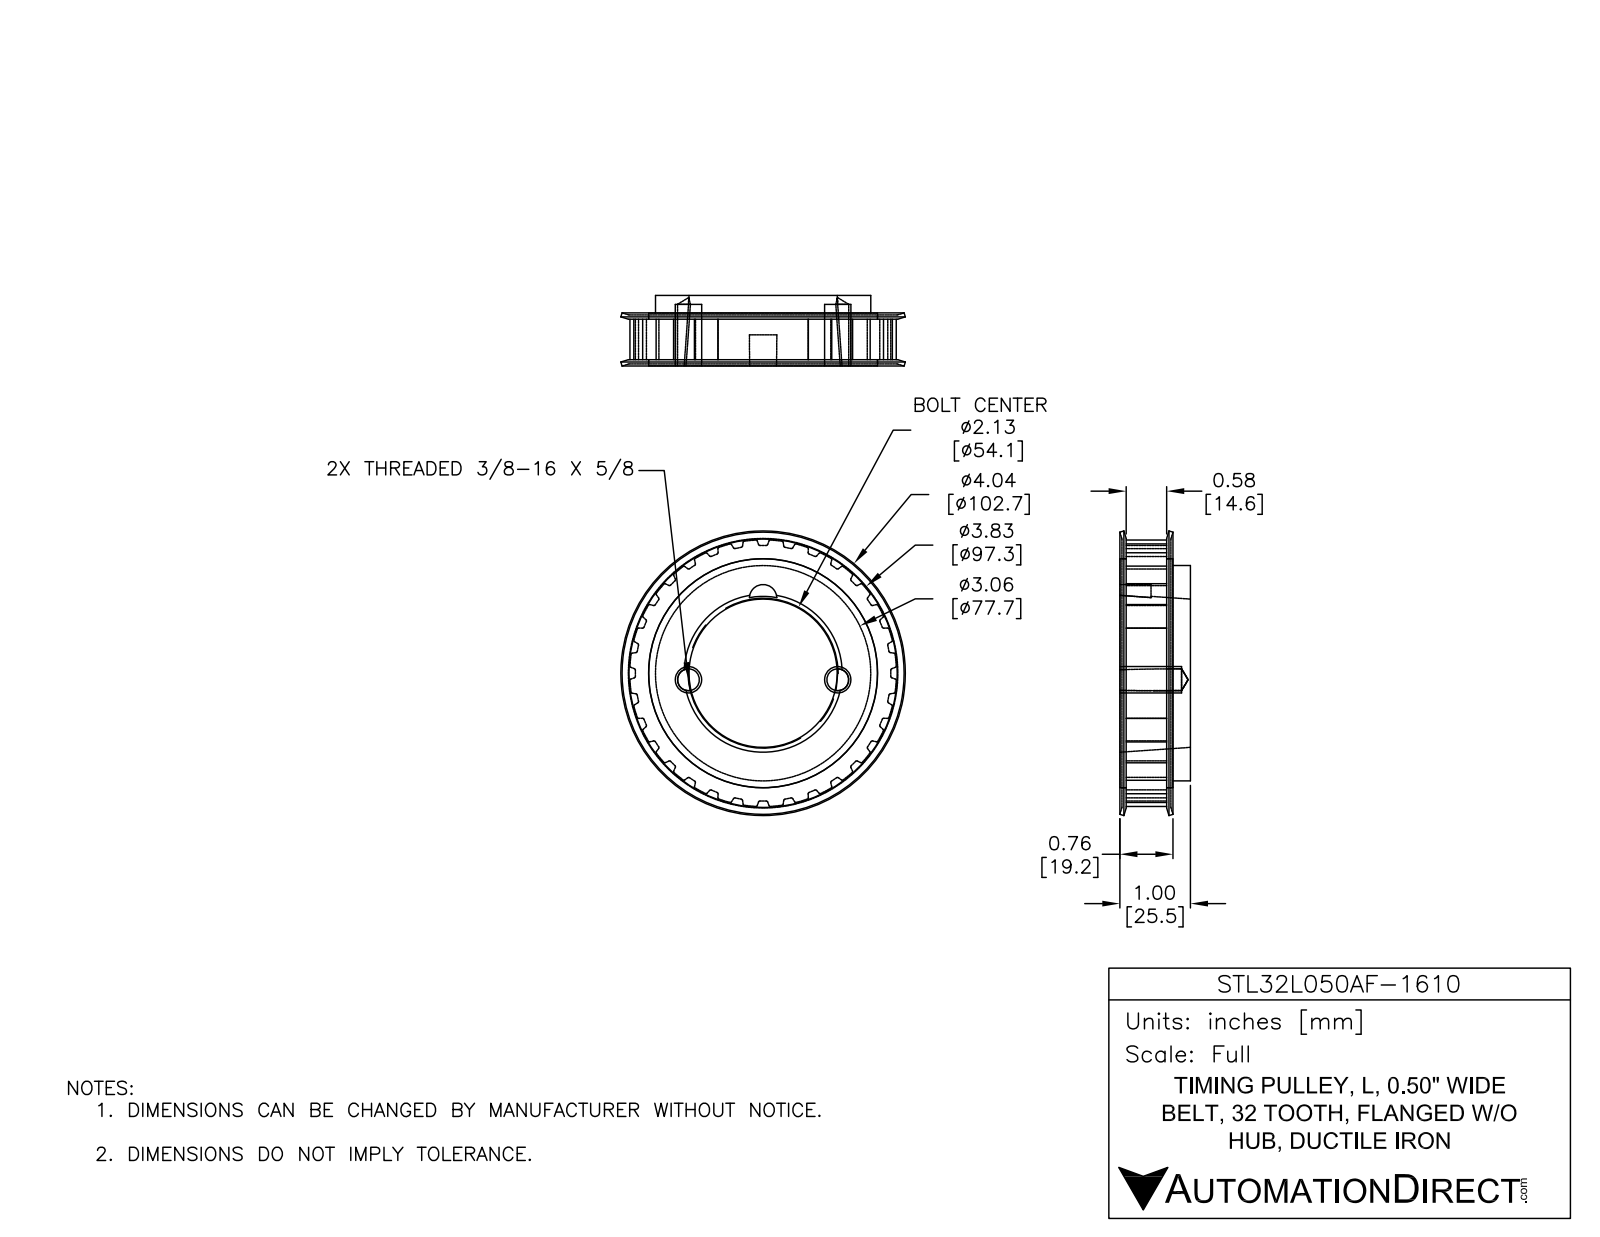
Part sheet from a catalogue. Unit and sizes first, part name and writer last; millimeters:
Units: millimetres
Overall size (bounding box): 102.72 × 102.72 × 25.46
Round holes (diameter × count): ⌀82.65 ×1
Round bosses / shafts (diameter × count): ⌀82.56 ×1, ⌀77.72 ×1
Partial cylindrical surfaces — rounded edges, fillets, slot ends (radius × count): R0.38 ×64, R0.51 ×64, R3.94 ×2, R4.95 ×1, R48.13 ×1
Main face-to-face distances: 25.4, 7.05, 24.71, 17.66, 18.35, 0.69, 1.53, 16.13, 6.35, 0.7
Volume: 103 270 mm³ · Surface area: 28 822 mm²
Bodies: 1 solid, 324 faces (106 planar, 200 cylindrical, 18 other)
Part name (STEP PRODUCT): STL32L050AF-1610
STEP written by: SolidWorks 2018 (AUTOMOTIVE_DESIGN)
